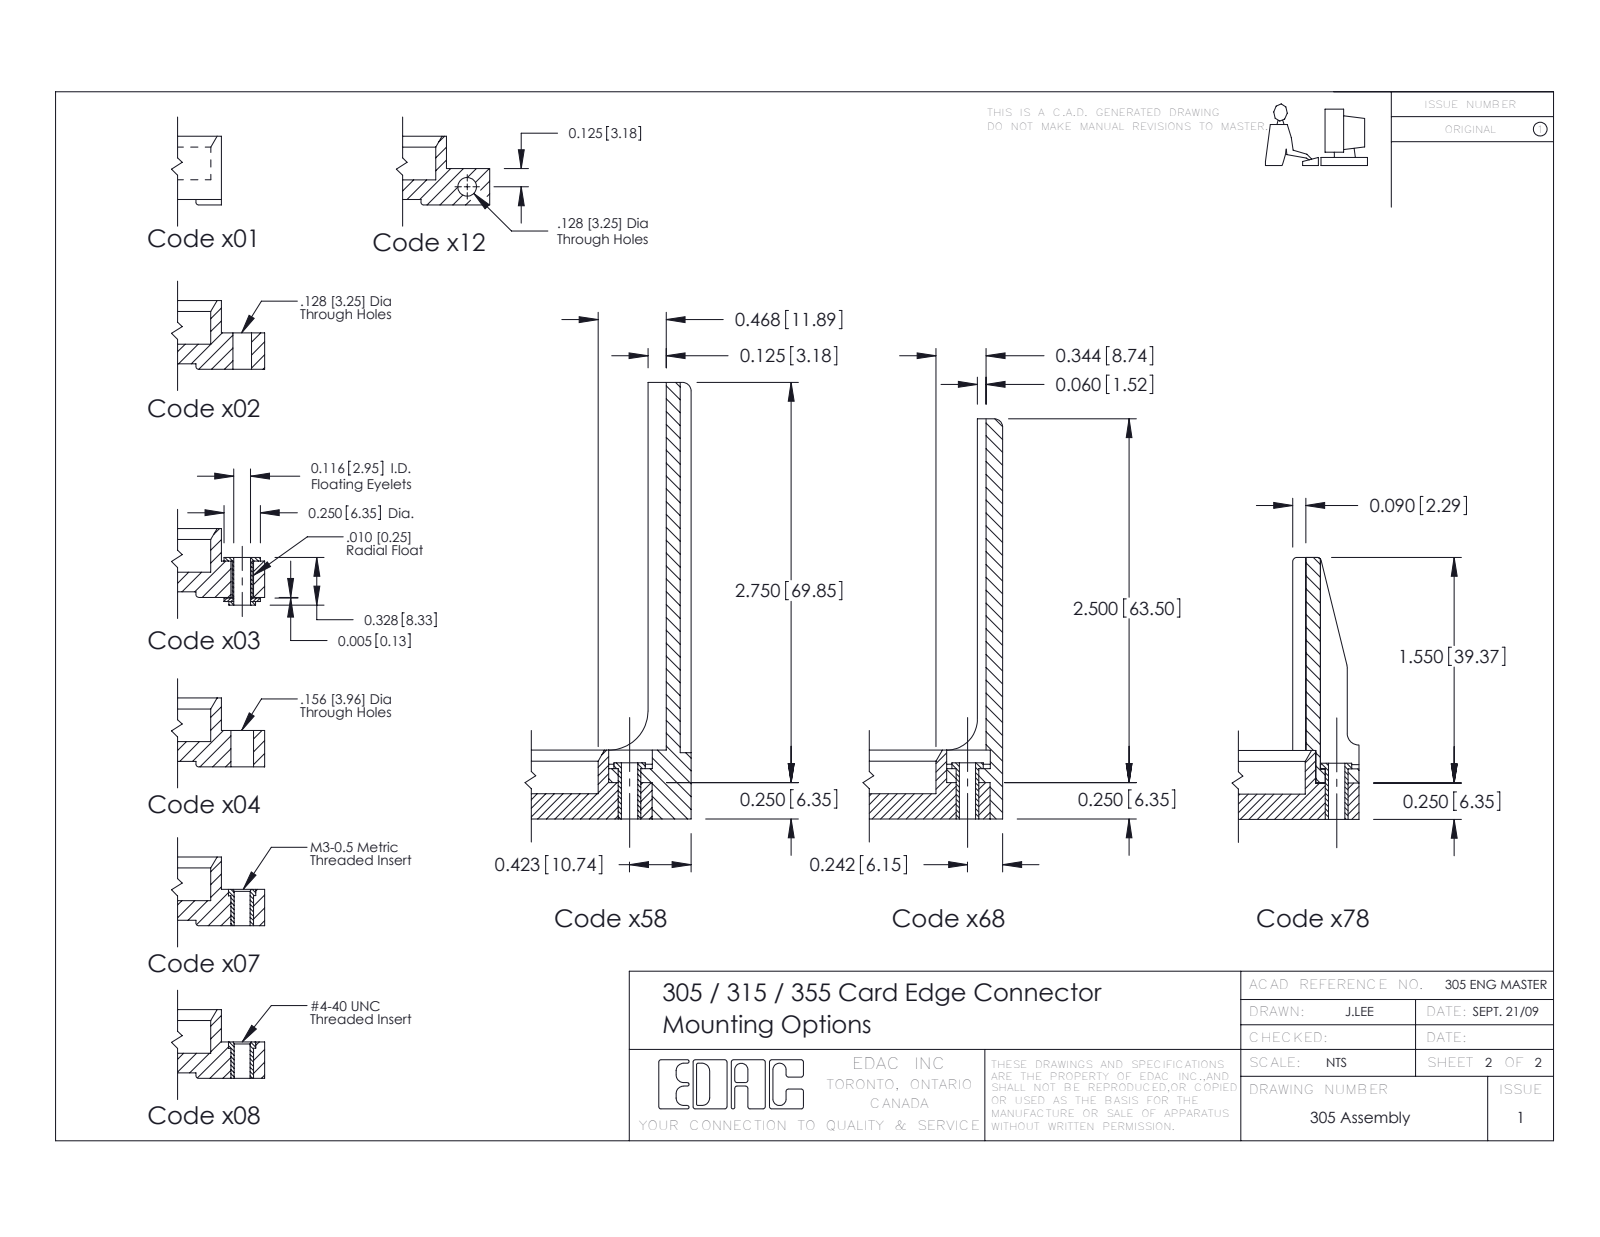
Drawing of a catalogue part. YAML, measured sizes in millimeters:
part_name: "315-014-500-202; 305-290-001_500; 305 Part_.128 Dia"
step_written_by: "SolidWorks 2016 (CONFIG_CONTROL_DESIGN)"
units: millimeters
bodies: {solids: 15, faces: 816, planar: 460, cylindrical: 328, other: 28}
overall_size: [50.7, 18.8, 8.7]
volume: 3210
surface_area: 5176
round_holes:
  - {diameter: 3.3, count: 2}
partial_cylinders:
  - {radius: 0.4, count: 26}
  - {radius: 0.3, count: 22}
  - {radius: 0.6, count: 14}
  - {radius: 0.8, count: 14}
  - {radius: 0.2, count: 7}
  - {radius: 0.2, count: 6}
  - {radius: 0.8, count: 6}
  - {radius: 0.7, count: 3}
face_to_face_distances: [0.3, 4.5, 0.9, 8.7, 4, 1.3, 1.5, 7.2, 5.7, 7.2]
hole_center_spacings: [42.9]
